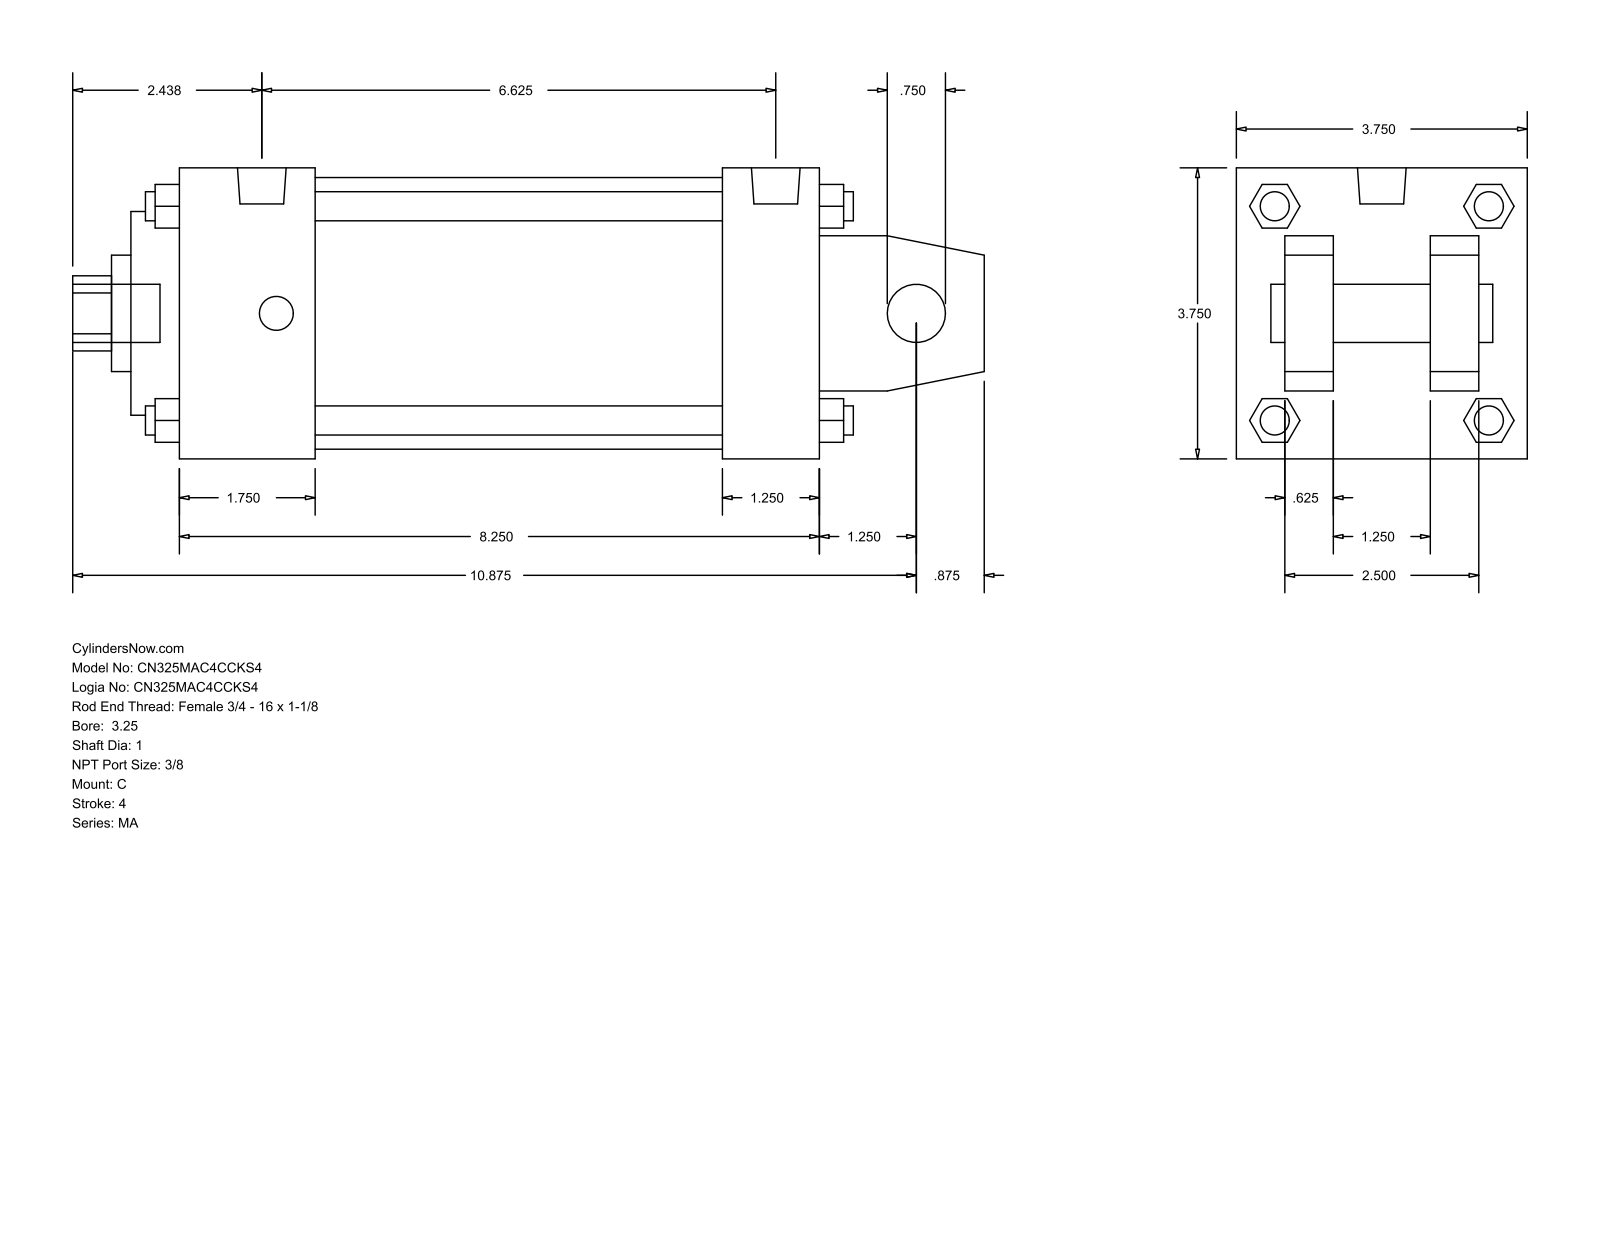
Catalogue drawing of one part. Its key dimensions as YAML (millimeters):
part_name: "MA_C__0325_1"
step_written_by: "GSSL Pune (CONFIG_CONTROL_DESIGN)"
units: millimeters
bodies: {solids: 0, faces: 141, planar: 109, cylindrical: 32, other: 0}
overall_size: [298.45, 95.25, 95.25]
round_holes:
  - {diameter: 19.05, count: 1}
  - {diameter: 25.4, count: 1}
  - {diameter: 38.1, count: 1}
  - {diameter: 66.67, count: 1}
  - {diameter: 88.9, count: 1}
round_bosses_or_shafts:
  - {diameter: 11.11, count: 4}
  - {diameter: 9.53, count: 4}
  - {diameter: 15.93, count: 2}
  - {diameter: 19.05, count: 1}
partial_cylinders:
  - {radius: 12.29, count: 1}
face_to_face_distances: [95.24, 15.87, 63.5, 209.55, 31.74, 79.37, 47.63, 225.42, 177.8, 31.75]
